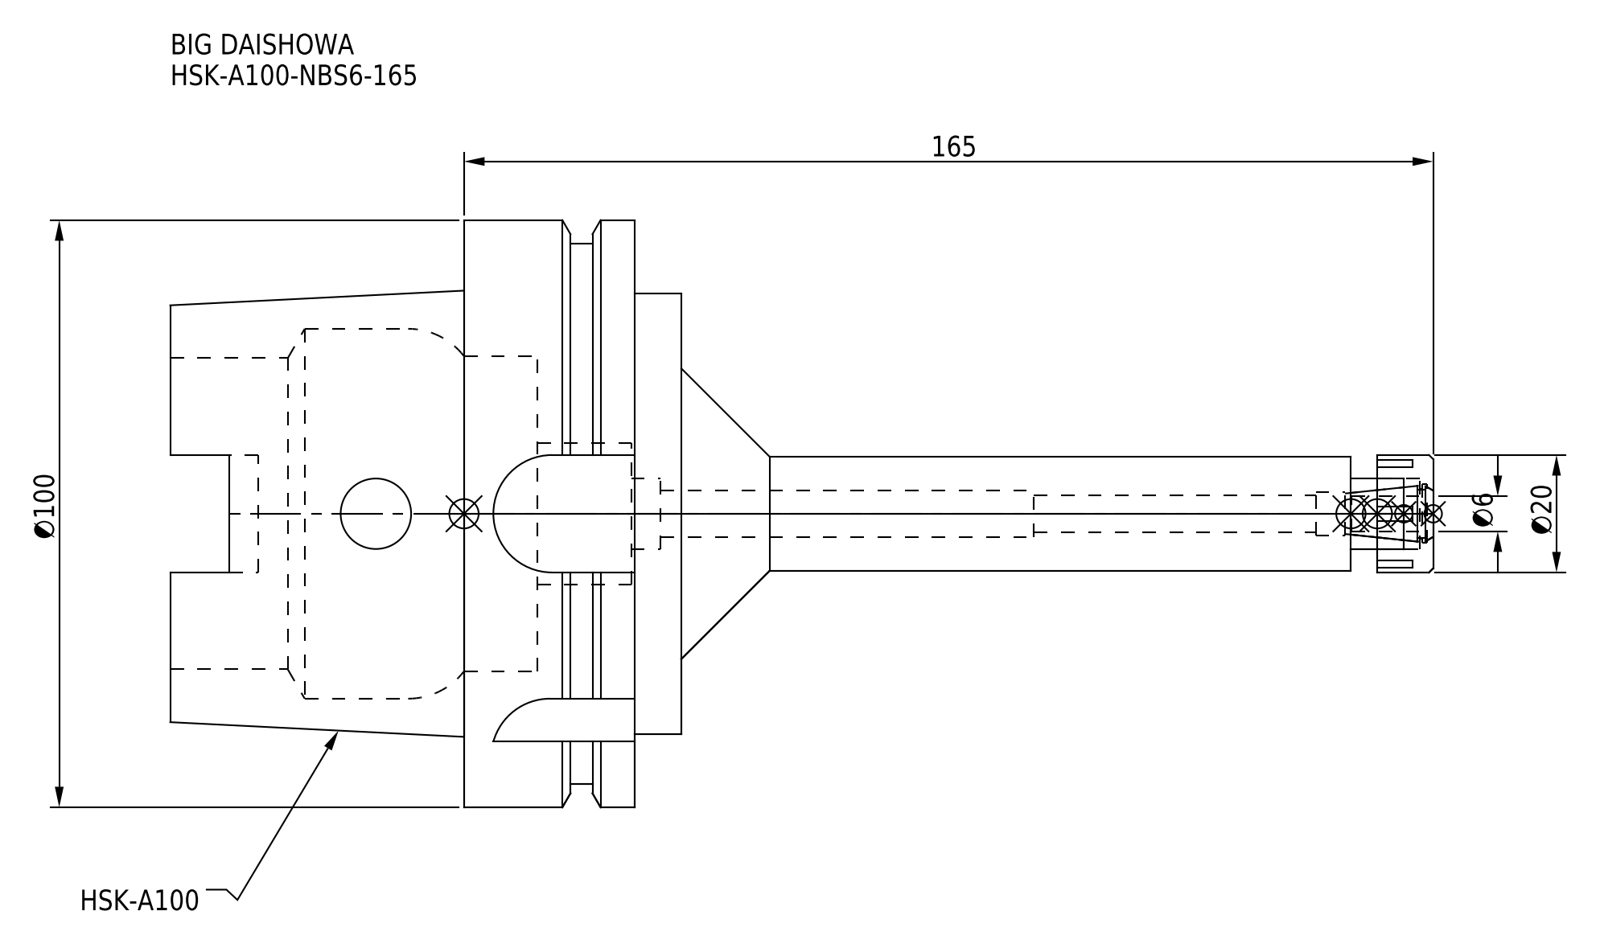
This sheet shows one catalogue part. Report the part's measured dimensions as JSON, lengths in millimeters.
{"part_name": "HSK-A100-NBS6-165_1.stp; NBN6_1.stp; HSK-A100-NBS6-165.stp; HA100NB06165-060_ASM.stp (+3 more)", "step_written_by": "SolidWorks 2019 (CONFIG_CONTROL_DESIGN)", "units": "millimeters", "bodies": {"solids": 2, "faces": 141, "planar": 67, "cylindrical": 52, "other": 22}, "overall_size": [215, 100, 100], "volume_mm3": 330301, "surface_area_mm2": 63576, "round_holes": [[12, 2], [6.4, 1], [7.5, 1], [8, 1], [8.5, 1], [10, 1], [24, 1], [53, 1], [53.8, 1], [63, 1]], "round_bosses_or_shafts": [[100, 1], [92, 1], [75, 1], [20, 1], [19.5, 1]], "partial_cylinders_radius": [[4.88, 4], [10, 4]], "face_to_face_distances": [29, 8, 37, 24.55, 16.55, 12.45, 87, 79, 62.45, 50]}
